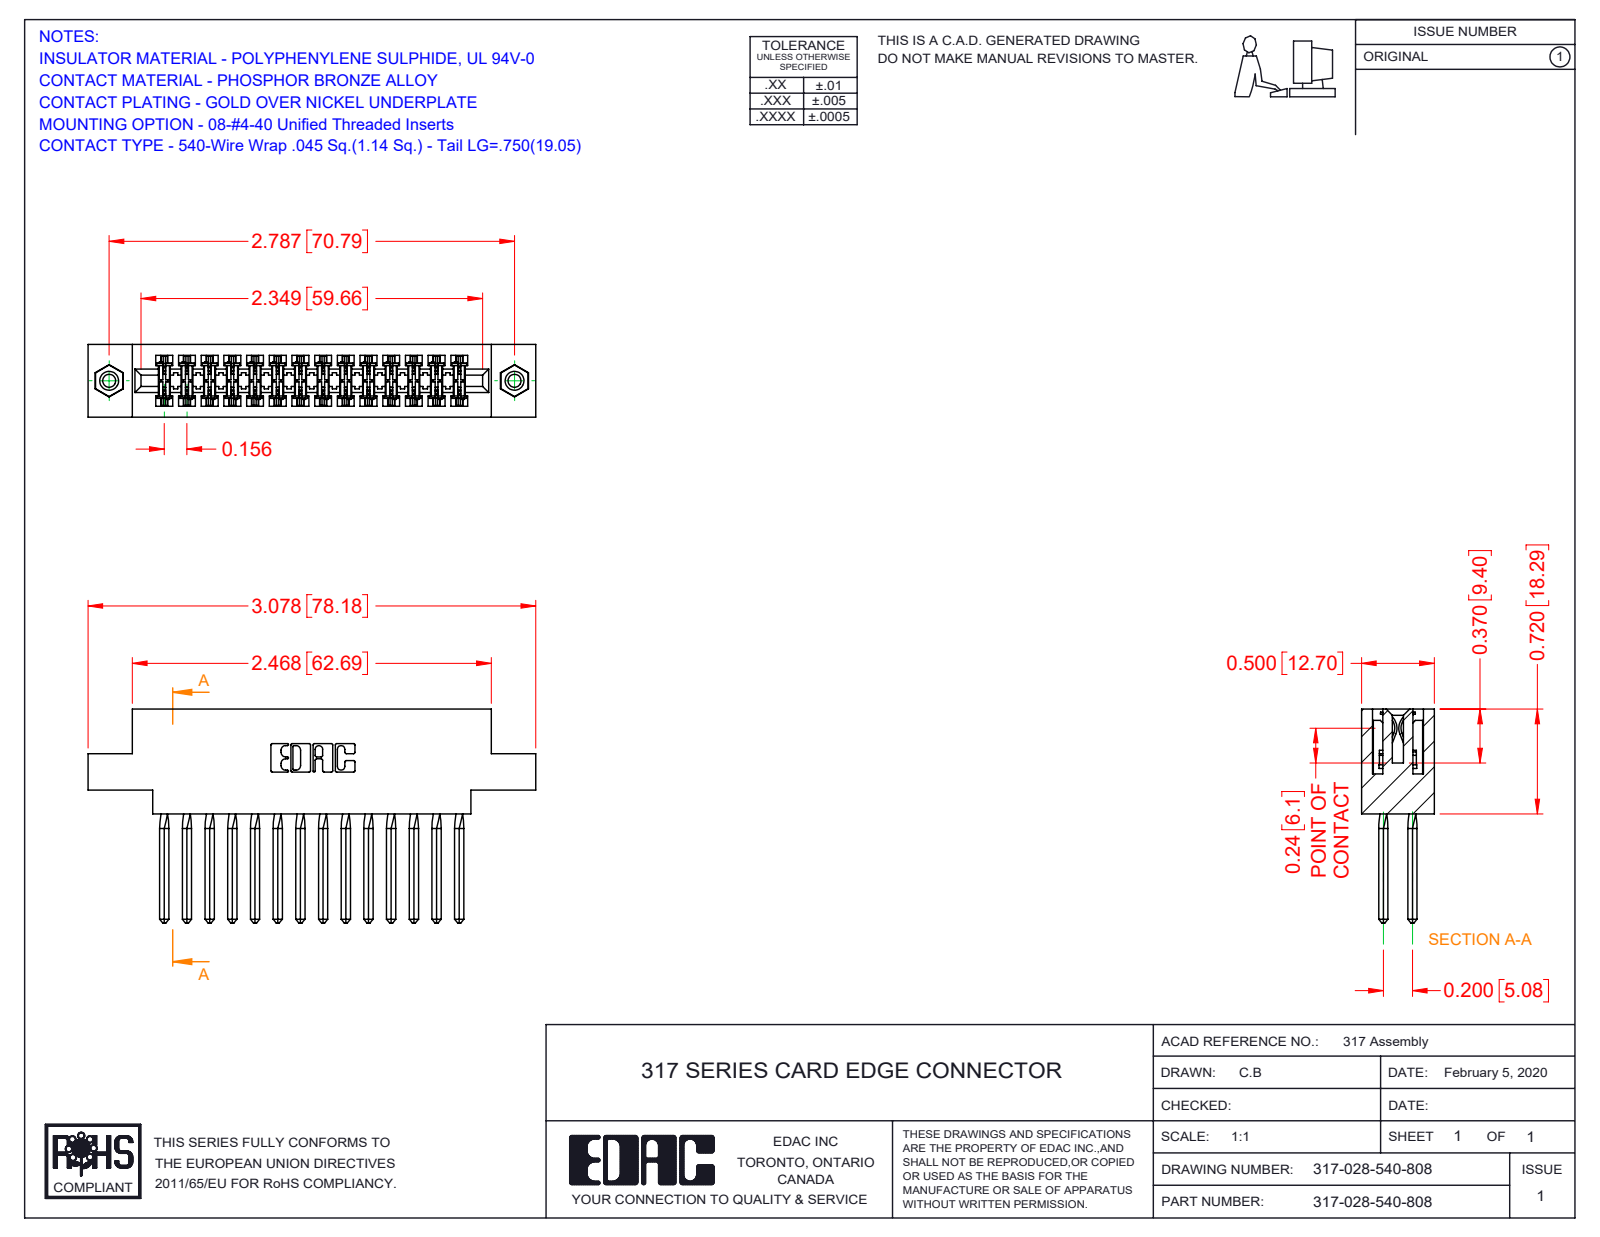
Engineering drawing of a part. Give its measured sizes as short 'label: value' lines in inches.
name: 317-028-540-878; 345-250-001_345-250-003-102; 317 Part_.156 Dia - TI; 317-290-001_540
written by: SolidWorks 2016 (CONFIG_CONTROL_DESIGN)
unit: in
bodies: 31 solids, 2654 faces (2134 planar, 392 cylindrical, 128 other)
size: 3.078 × 1.47 × 0.5
volume: 0.743 in³; area: 26.51 in²
holes: 2× ⌀0.089, 2× ⌀0.125, 2× ⌀0.156
bosses: 2× ⌀0.155
rounds: 56× R0.015, 22× R0.01, 6× R0.007, 6× R0.031, 3× R0.026, 2× R0.095, 2× R0.1, 2× R0.11
face distances: 0.5, 0.075, 0.425, 0.11, 0.35, 0.22, 0.136, 0.116, 0.72, 0.195
hole spacings: 2.787
